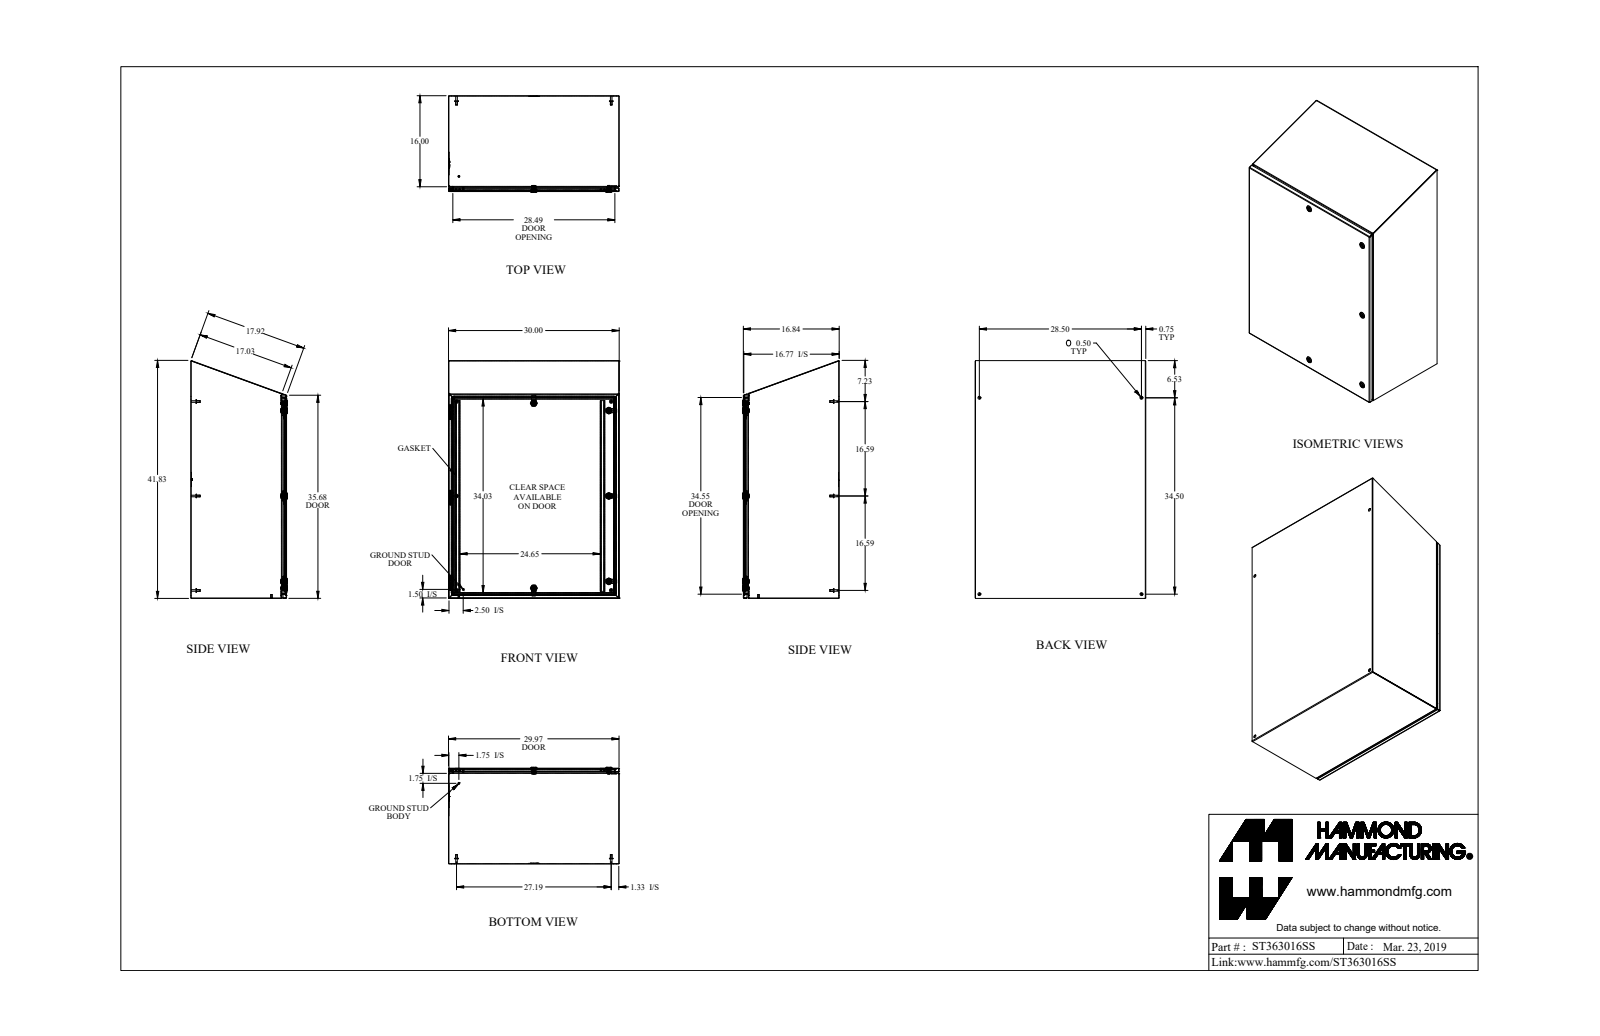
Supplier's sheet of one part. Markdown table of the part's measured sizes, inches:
| quantity | value |
| --- | --- |
| part name | ST363016SS |
| STEP written by | SolidWorks 2018 (AUTOMOTIVE_DESIGN) |
| units | inches |
| bodies | 52 solids, 1252 faces (683 planar, 383 cylindrical, 186 other) |
| overall size | 41.782 × 30 × 16.997 |
| volume | 366.1 in³ |
| surface area | 10 237 in² |
| round holes (diameter × count) | 0.5 × 9, 0.197 × 5, 0.387 × 5, 0.63 × 5, 0.768 × 5, 0.172 × 1, 0.24 × 1, 0.242 × 1 |
| round bosses / shafts (diameter × count) | 0.625 × 9, 0.313 × 8, 0.275 × 6, 1.1 × 5, 0.785 × 5, 0.525 × 5, 0.236 × 5, 0.625 × 2 |
| partial cylindrical surfaces (radius × count) | 0.036 × 18, 0.108 × 18, 0.01 × 12, 0.048 × 12, 0.125 × 10, 0.062 × 7, 0.006 × 6, 0.188 × 5 |
| main face-to-face distances | 0.072, 16.765, 29.928, 16.693, 16.837, 29.856, 30, 0.837, 15.928, 0.038 |
| hole center spacings | 15, 27.519, 28.5, 34.5, 44.749, 2.492, 2.494, 13.242 |
